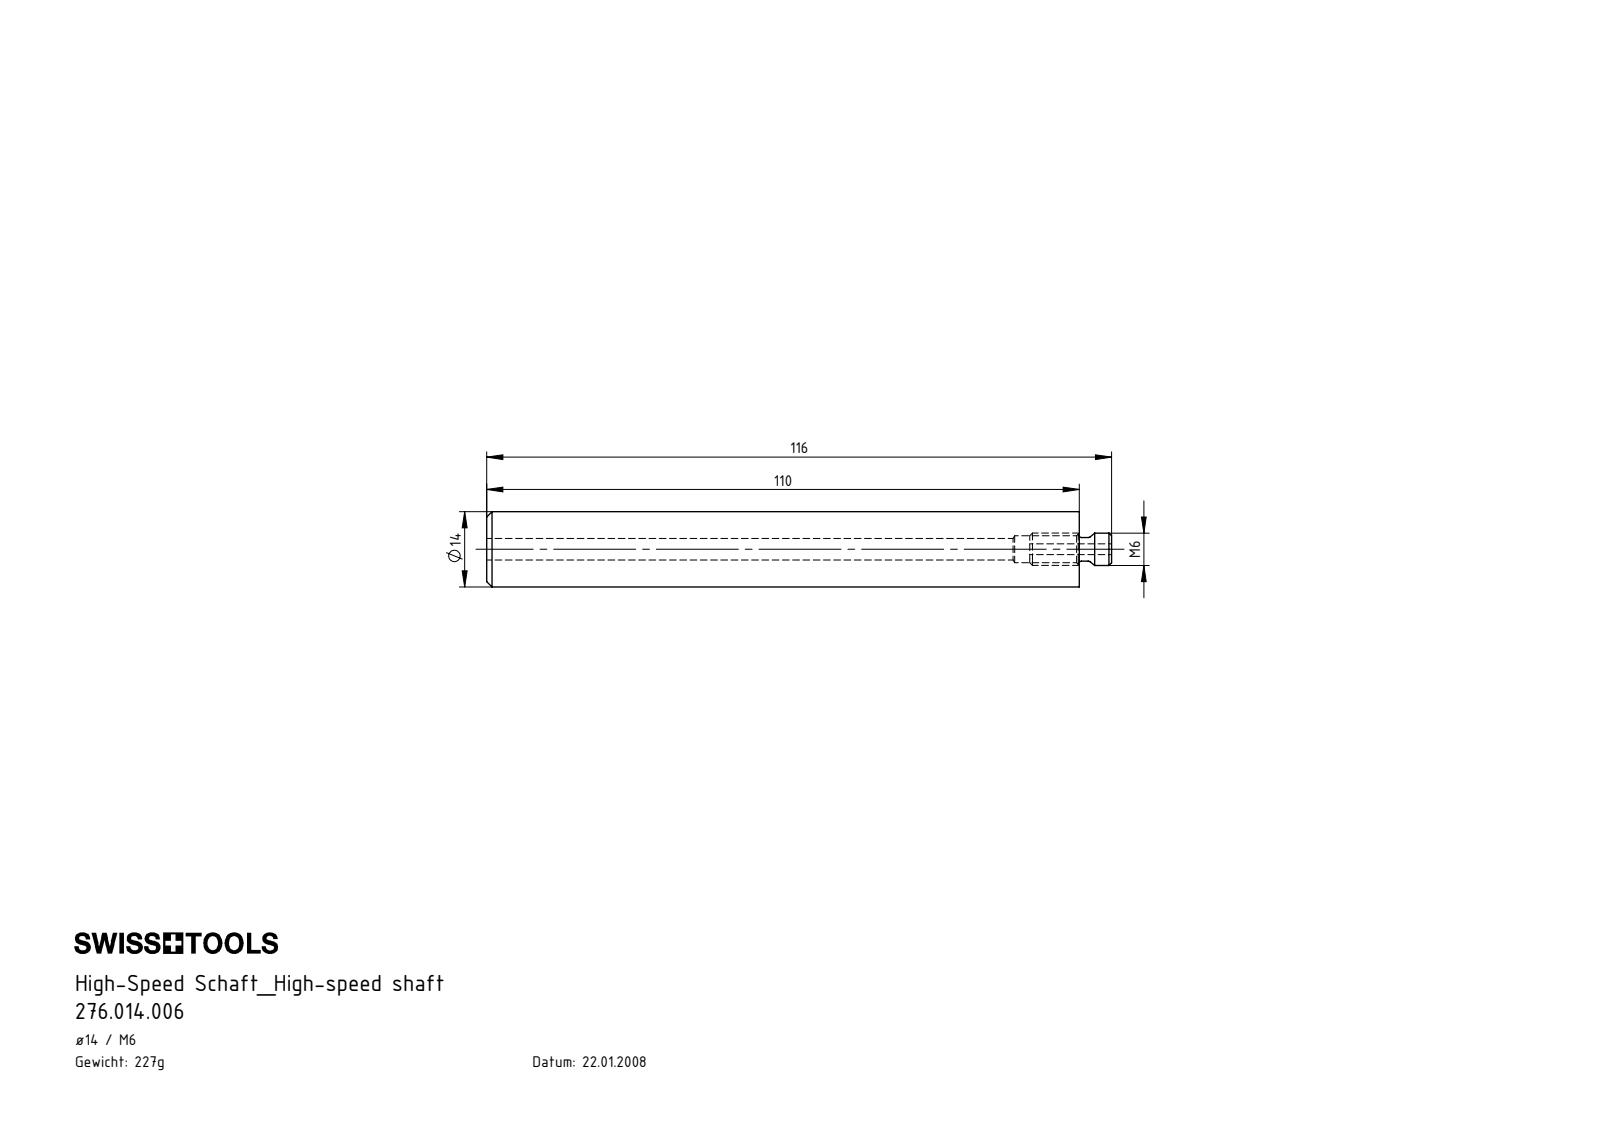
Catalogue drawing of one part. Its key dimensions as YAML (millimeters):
part_name: "276.014.006; HM1-U14.001.110_A; HM1-BG1.006.015_A"
step_written_by: "SolidWorks 2017 (CONFIG_CONTROL_DESIGN)"
units: millimeters
bodies: {solids: 2, faces: 35, planar: 5, cylindrical: 14, other: 16}
overall_size: [116, 14, 14]
volume: 15787
surface_area: 6929
round_holes:
  - {diameter: 2, count: 1}
  - {diameter: 4, count: 1}
  - {diameter: 5, count: 1}
round_bosses_or_shafts:
  - {diameter: 14, count: 1}
  - {diameter: 6, count: 1}
  - {diameter: 4.4, count: 1}
face_to_face_distances: [110, 100.8, 116, 9.2, 15.2, 6, 109.8, 9, 6.2]
